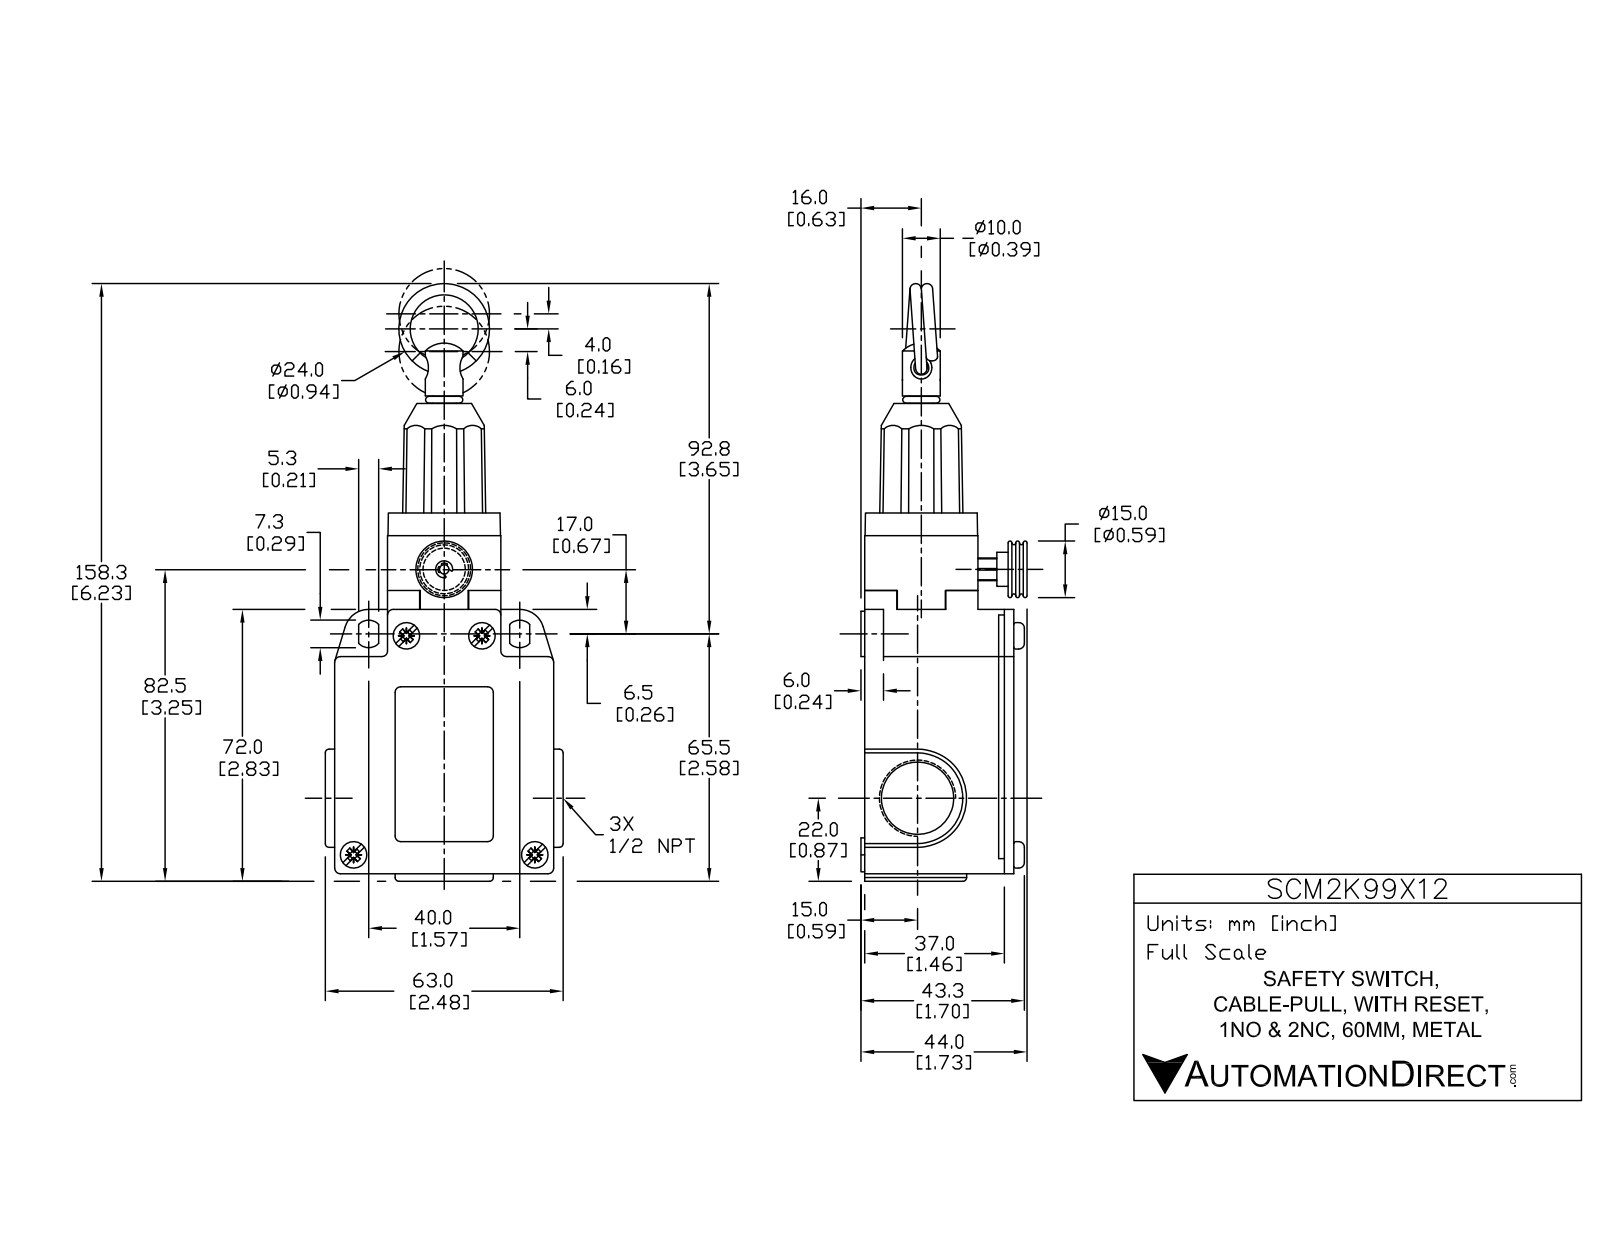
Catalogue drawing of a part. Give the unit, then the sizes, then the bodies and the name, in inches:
Units: inches
Overall size (bounding box): 6.28 × 2.441 × 1.724
Round holes (diameter × count): ⌀0.669 ×2, ⌀0.748 ×2, ⌀0.157 ×1, ⌀0.398 ×1, ⌀0.709 ×1
Round bosses / shafts (diameter × count): ⌀0.276 ×4, ⌀0.472 ×2, ⌀0.354 ×2, ⌀0.701 ×1, ⌀0.394 ×1, ⌀0.386 ×1, ⌀0.264 ×1, ⌀0.248 ×1
Partial cylindrical surfaces — rounded edges, fillets, slot ends (radius × count): R0.059 ×12, R0.144 ×2, R0.256 ×2, R0.512 ×2, R0.453 ×1, R0.472 ×1
Main face-to-face distances: 1.555, 0.551, 1.732, 1.181, 2.283, 0.079, 0.236, 0.157, 0.197, 2.756
Hole centre spacings: 0.039, 4.528
Volume: 11.03 in³ · Surface area: 50.03 in²
Bodies: 5 solids, 256 faces (100 planar, 94 cylindrical, 62 other)
Part name (STEP PRODUCT): SCM2K99X12
STEP written by: SolidWorks 2017 (AUTOMOTIVE_DESIGN)
